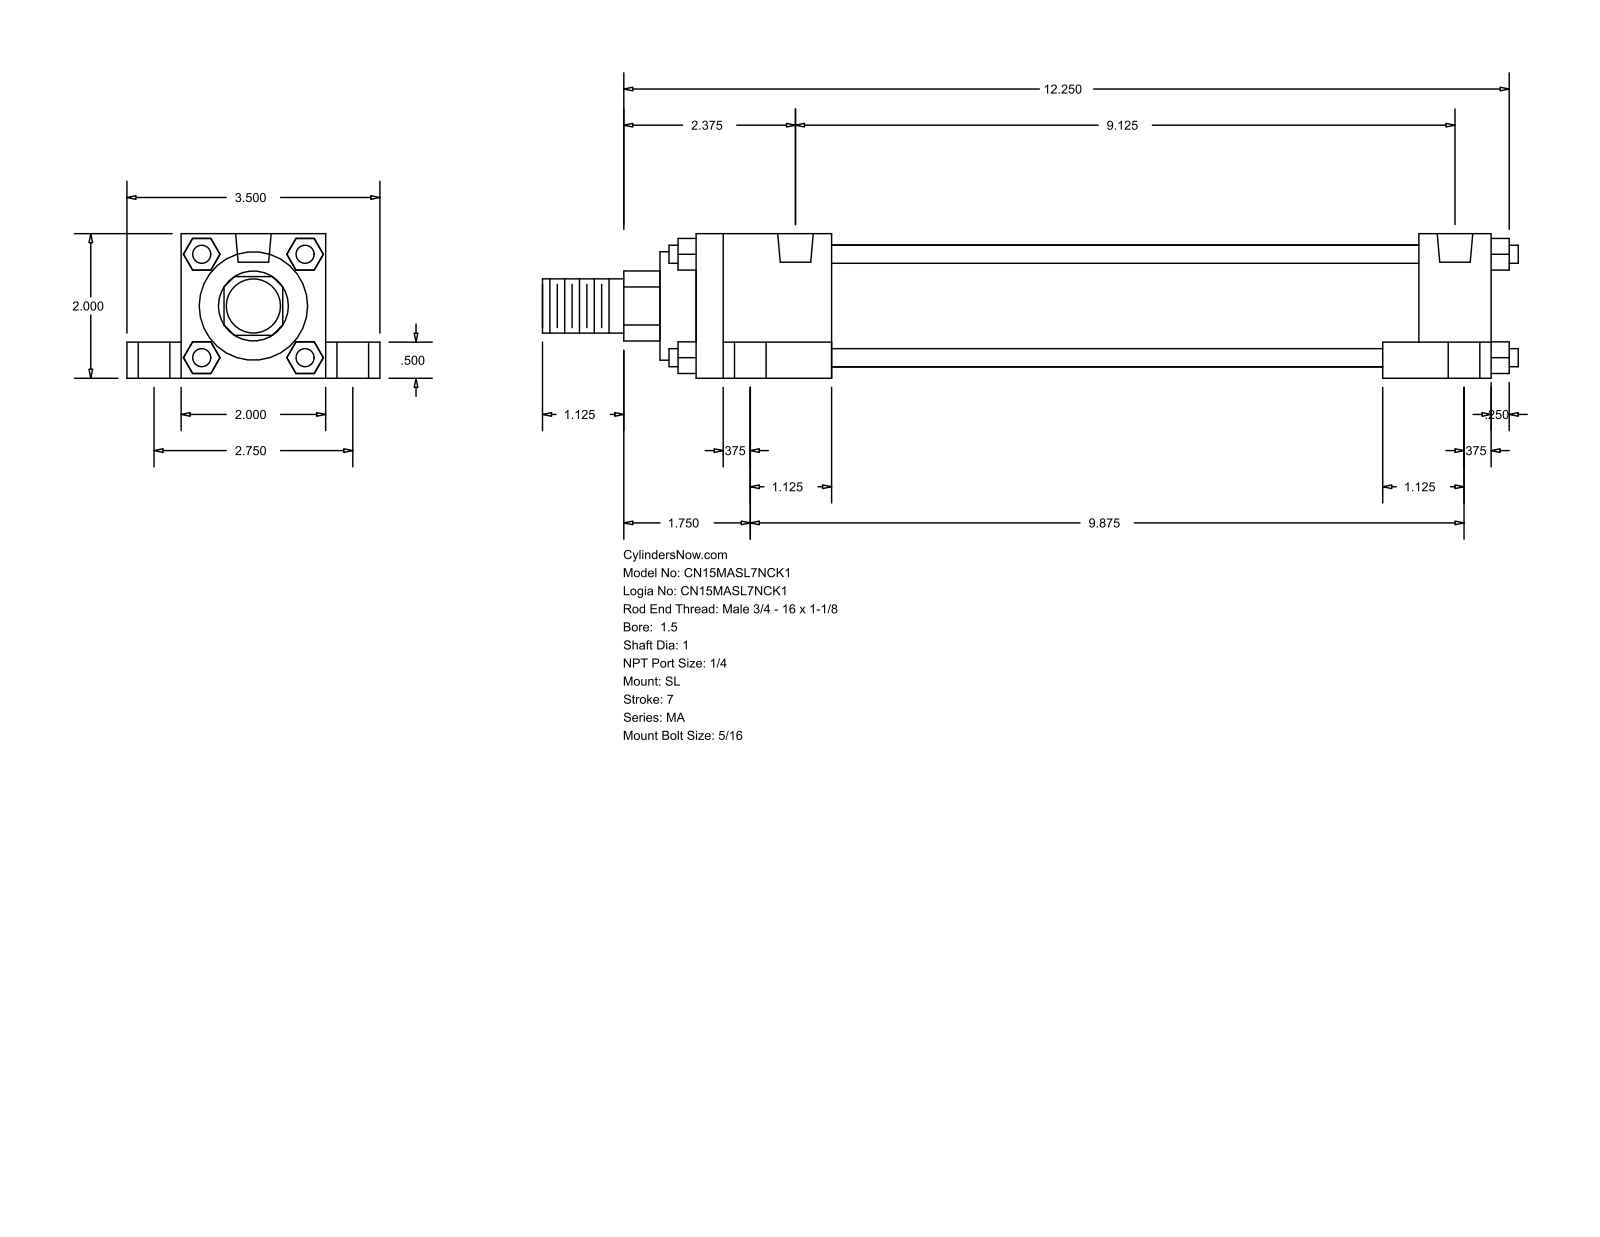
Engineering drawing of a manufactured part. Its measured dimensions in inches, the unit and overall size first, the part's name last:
Units: inches
Overall size (bounding box): 13.5 × 3.5 × 2
Round holes (diameter × count): ⌀0.313 ×4, ⌀0.437 ×4, ⌀0.687 ×4, ⌀0.492 ×2
Round bosses / shafts (diameter × count): ⌀0.25 ×4, ⌀1.69 ×1, ⌀1.5 ×1, ⌀1 ×1, ⌀0.75 ×1
Partial cylindrical surfaces — rounded edges, fillets, slot ends (radius × count): R0.484 ×1
Main face-to-face distances: 2, 0.5, 0.75, 2.75, 1.5, 0.375, 11, 1, 0.25, 10
Hole centre spacings: 1.38, 1.51, 2.75, 9.125, 9.351, 9.846, 9.875, 10.25
Bodies: 0 solids, 148 faces (112 planar, 36 cylindrical, 0 other)
Part name (STEP PRODUCT): MA_SL__0150_1
STEP written by: GSSL Pune (CONFIG_CONTROL_DESIGN)
